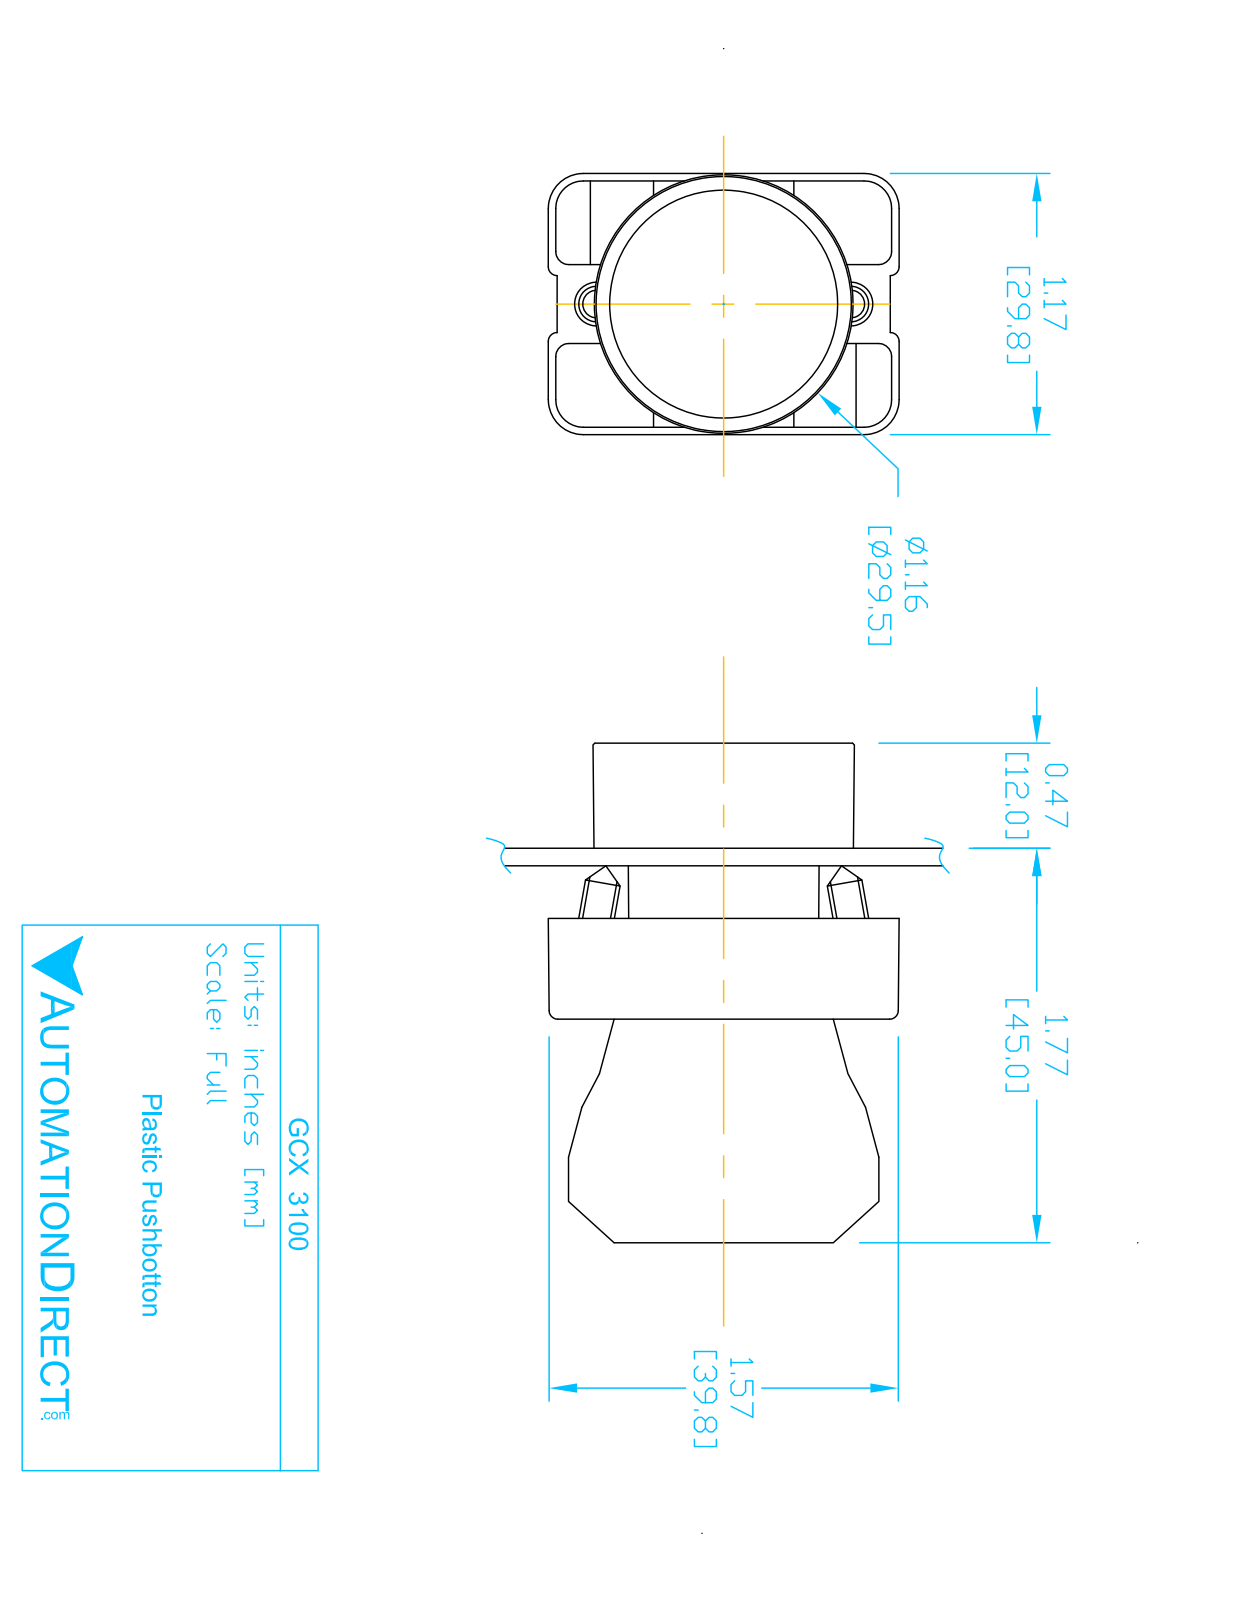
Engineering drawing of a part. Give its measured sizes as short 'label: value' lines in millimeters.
name: GCX3100; ECX3029-2; ecx1040; GCX3100 OPERATOR
written by: SolidWorks 2016 (AUTOMOTIVE_DESIGN)
unit: mm
bodies: 6 solids, 381 faces (222 planar, 132 cylindrical, 27 other)
size: 56.3 × 40.2 × 29.9
volume: 28 530 mm³; area: 17 510 mm²
holes: 2× ⌀2, 2× ⌀3.1, 2× ⌀3.3, 1× ⌀2.2, 1× ⌀5, 1× ⌀22.3, 1× ⌀22.6, 1× ⌀26
bosses: 2× ⌀4, 1× ⌀29.8, 1× ⌀25.5, 1× ⌀24, 1× ⌀21.7, 1× ⌀19.8
rounds: 24× R1.5, 12× R1, 12× R3.1, 12× R4, 4× R1, 2× R3.3, 1× R0.5, 1× R1.6
face distances: 18.3, 14.7, 0.8, 12, 30.3, 0.8, 17.5, 15.2, 29.5, 27.2
hole spacings: 6, 13.8, 12, 12.4
